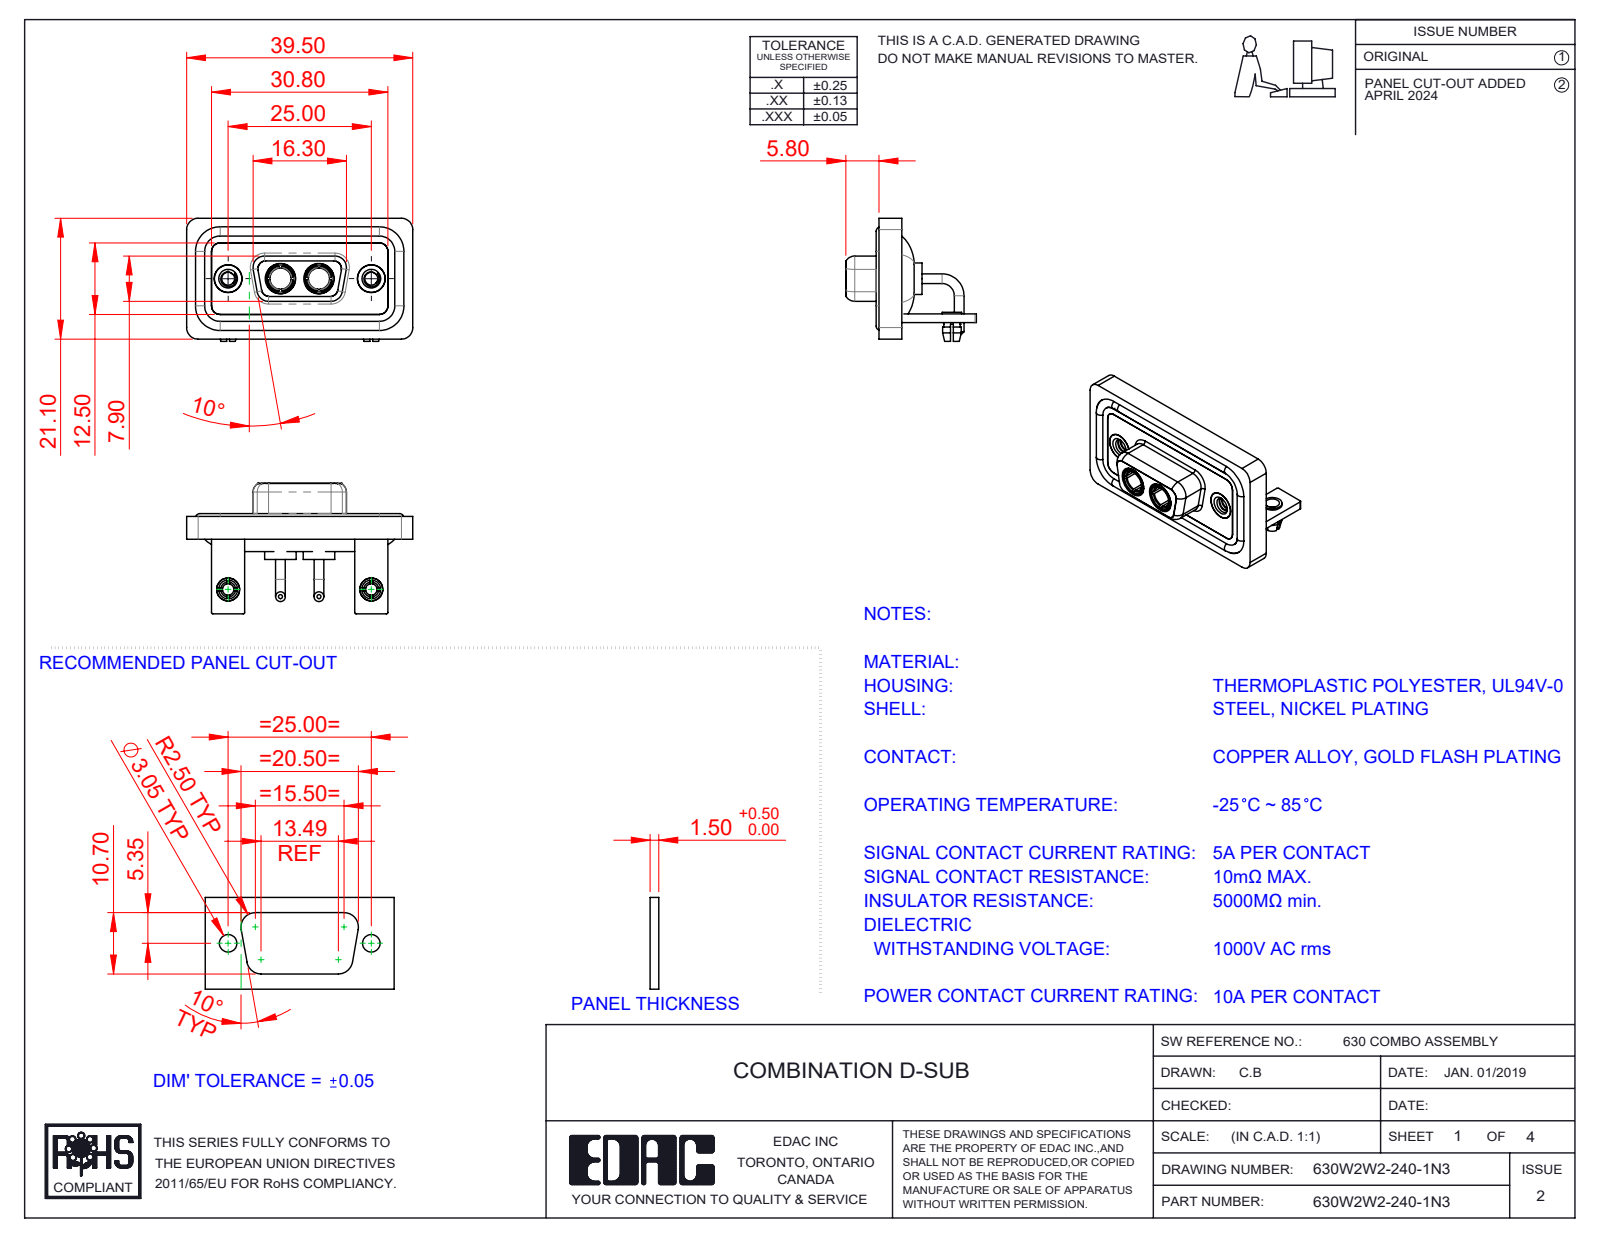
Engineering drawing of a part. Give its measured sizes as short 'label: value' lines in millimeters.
name: 630W2W2-140-1N3; 630Combo Shell Rear_09 Contacts; 630Combo Threaded Rivet_2; 630Combo Board Lock_50 Contacts (+5 more)
written by: SolidWorks 2023 (CONFIG_CONTROL_DESIGN)
unit: mm
bodies: 15 solids, 682 faces (231 planar, 294 cylindrical, 157 other)
size: 39.5 × 22.8 × 21.5
volume: 5 103 mm³; area: 8 630 mm²
holes: 4× ⌀4.85, 2× ⌀2, 2× ⌀2.26, 2× ⌀2.5, 2× ⌀3.2, 2× ⌀3.7, 2× ⌀4, 2× ⌀4.05, 2× ⌀5, 2× ⌀5.3
bosses: 4× ⌀1.7, 4× ⌀1.6, 2× ⌀5.5, 2× ⌀5.2, 2× ⌀4.96, 2× ⌀4.95, 2× ⌀4.8, 2× ⌀4.75
rounds: 19× R2, 18× R1.5, 16× R0.25, 8× R1.35, 8× R1.6, 5× R0.5, 4× R0.6, 4× R0.65
face distances: 0.4, 2.9, 1.5, 1.8, 1.1, 3.7, 0.8, 2.5, 1.6, 3.1
hole spacings: 9.14, 15.86, 25, 6.72
